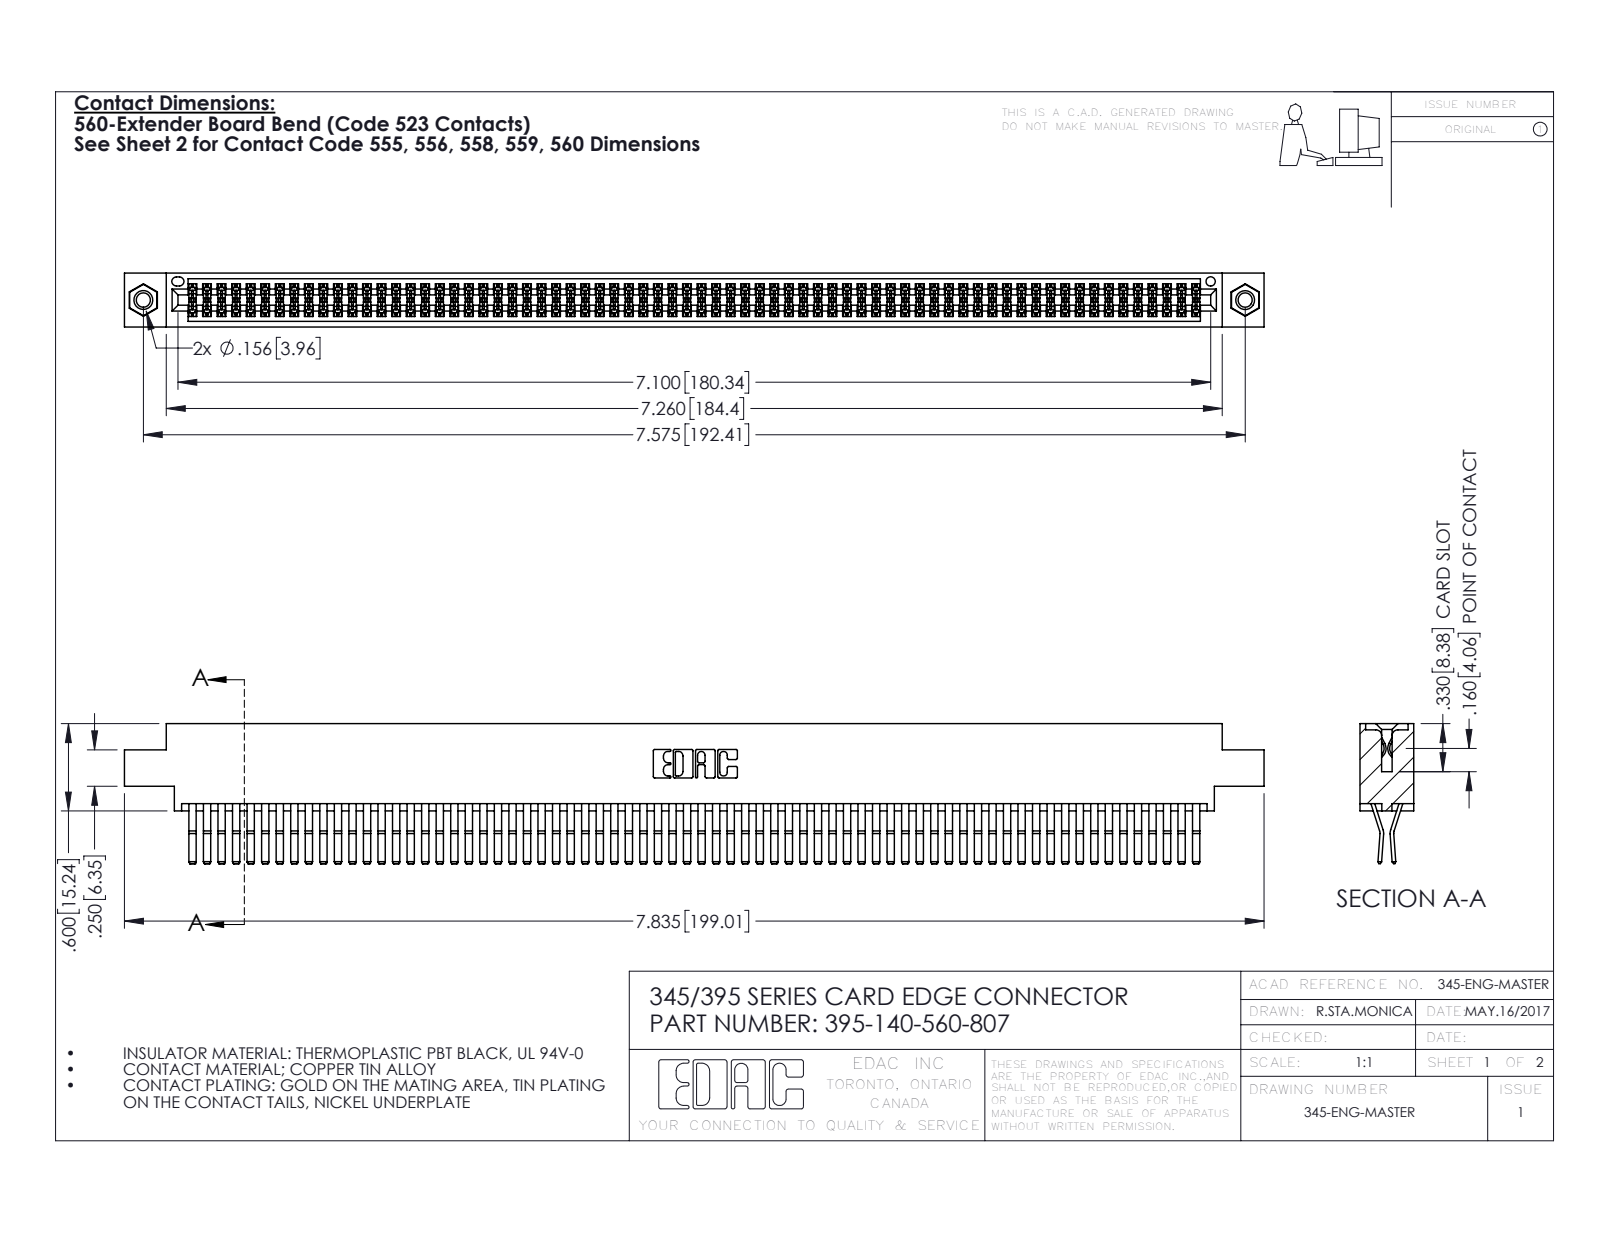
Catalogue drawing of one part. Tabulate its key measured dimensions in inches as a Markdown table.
| quantity | value |
| --- | --- |
| part name | 345-250-001_345-250-005-103; 345-292-001_560 Tail; 395-140-560-807; 345 Part_0.170 Offset - 0.156 Dia-TI |
| STEP written by | SolidWorks 2016 (CONFIG_CONTROL_DESIGN) |
| units | inches |
| bodies | 143 solids, 7470 faces (4736 planar, 2718 cylindrical, 16 other) |
| overall size | 7.835 × 0.962 × 0.37 |
| volume | 1.244 in³ |
| surface area | 51.46 in² |
| round holes (diameter × count) | 0.098 × 2, 0.125 × 2, 0.156 × 2, 0.064 × 1 |
| round bosses / shafts (diameter × count) | 0.155 × 2 |
| partial cylindrical surfaces (radius × count) | 0.006 × 210, 0.01 × 22, 0.007 × 6, 0.031 × 6, 0.026 × 3, 0.01 × 2, 0.014 × 2, 0.019 × 2 |
| main face-to-face distances | 0.025, 0.072, 0.298, 0.37, 0.2, 0.098, 0.272, 0.225, 0.175, 0.149 |
| hole center spacings | 0.27, 7.339, 7.575 |
